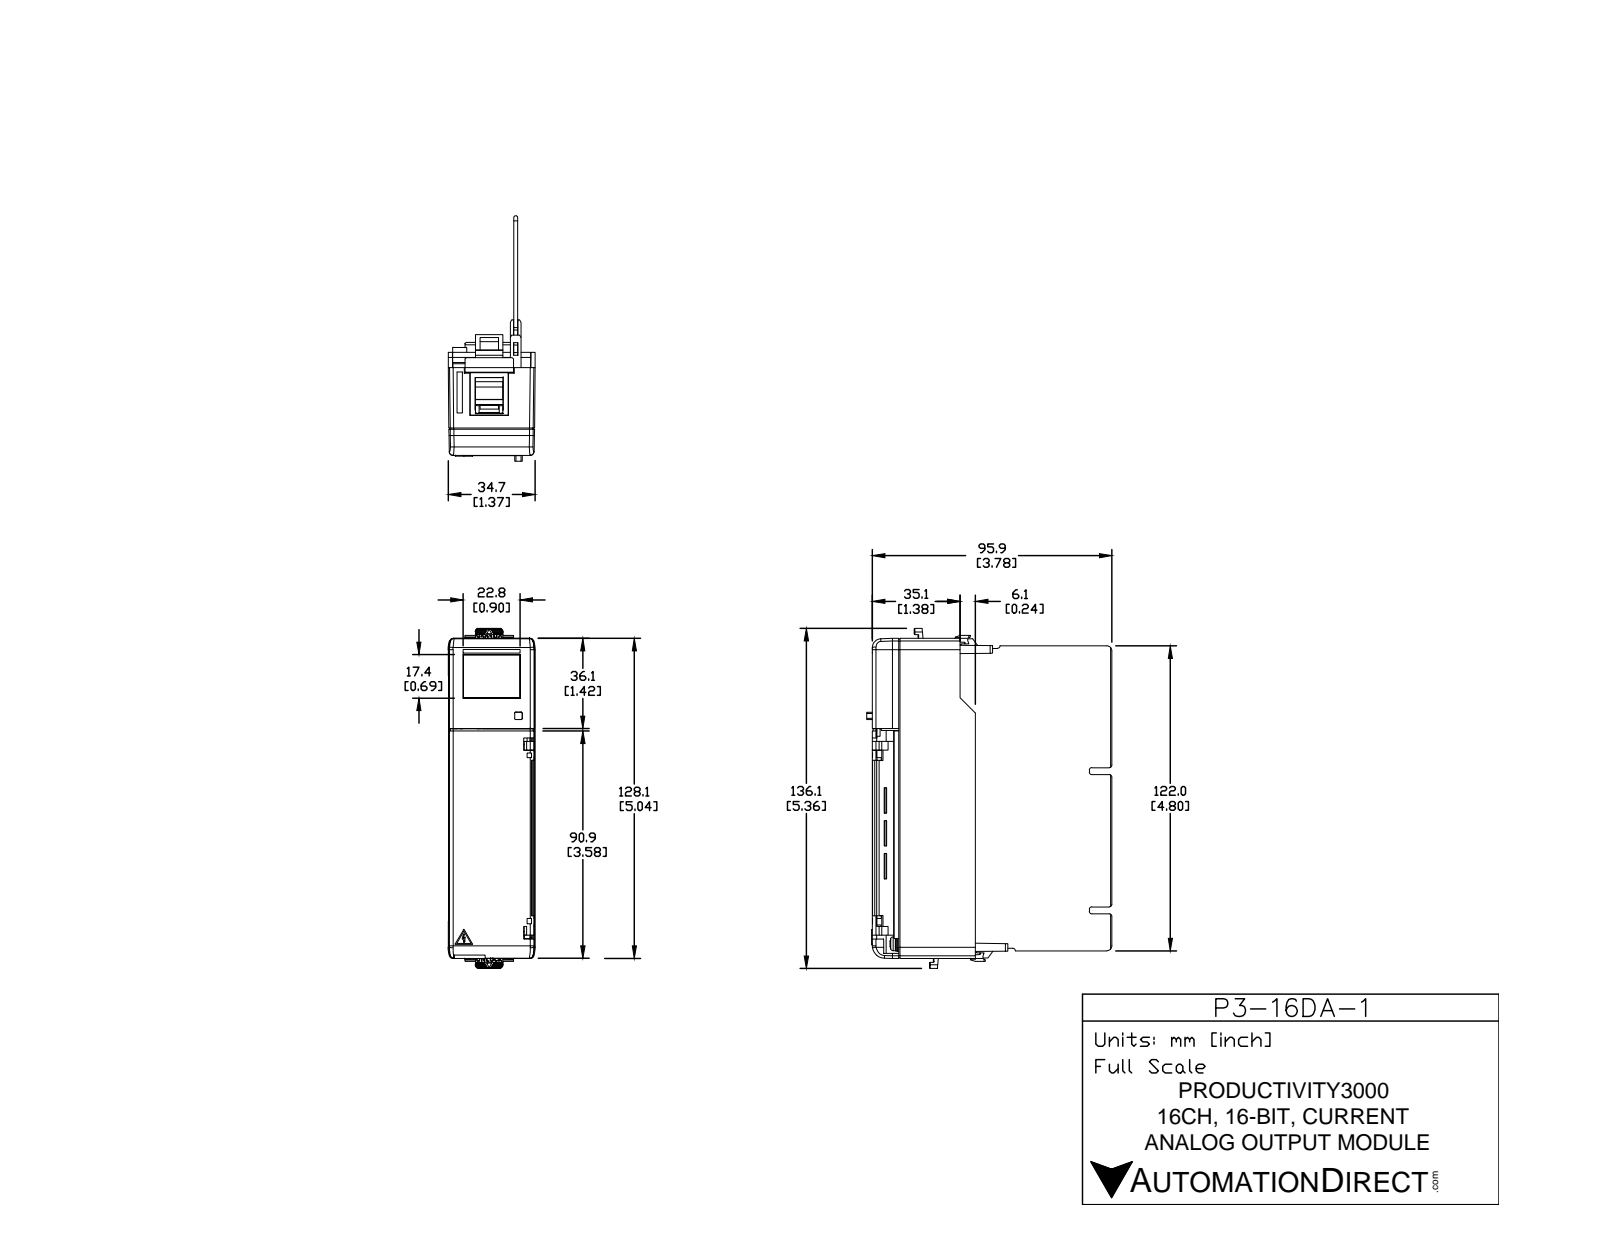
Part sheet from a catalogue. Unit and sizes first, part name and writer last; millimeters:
Units: millimetres
Overall size (bounding box): 136.08 × 98.18 × 34.8
Round holes (diameter × count): ⌀3.2 ×22, ⌀5 ×2, ⌀1.8 ×1
Round bosses / shafts (diameter × count): ⌀5.5 ×22, ⌀3 ×22, ⌀2.4 ×20, ⌀5.6 ×2, ⌀2.2 ×2, ⌀2 ×2, ⌀1.5 ×1
Partial cylindrical surfaces — rounded edges, fillets, slot ends (radius × count): R0.5 ×95, R1 ×33, R0.3 ×29, R1.67 ×22, R1.5 ×13, R2 ×6, R0.2 ×5, R0.1 ×4
Main face-to-face distances: 1.6, 1.7, 28.23, 26.53, 32.56, 22.2, 2.2, 7.9, 6.8, 5.32
Hole centre spacings: 8.68, 7.62, 13.84, 15.24, 20.59, 22.86, 27.79, 30.48
Volume: 101 360 mm³ · Surface area: 75 361 mm²
Bodies: 1 solid, 3823 faces (2833 planar, 744 cylindrical, 246 other)
Part name (STEP PRODUCT): P3-16DA-1
STEP written by: SolidWorks 2009 (CONFIG_CONTROL_DESIGN)
